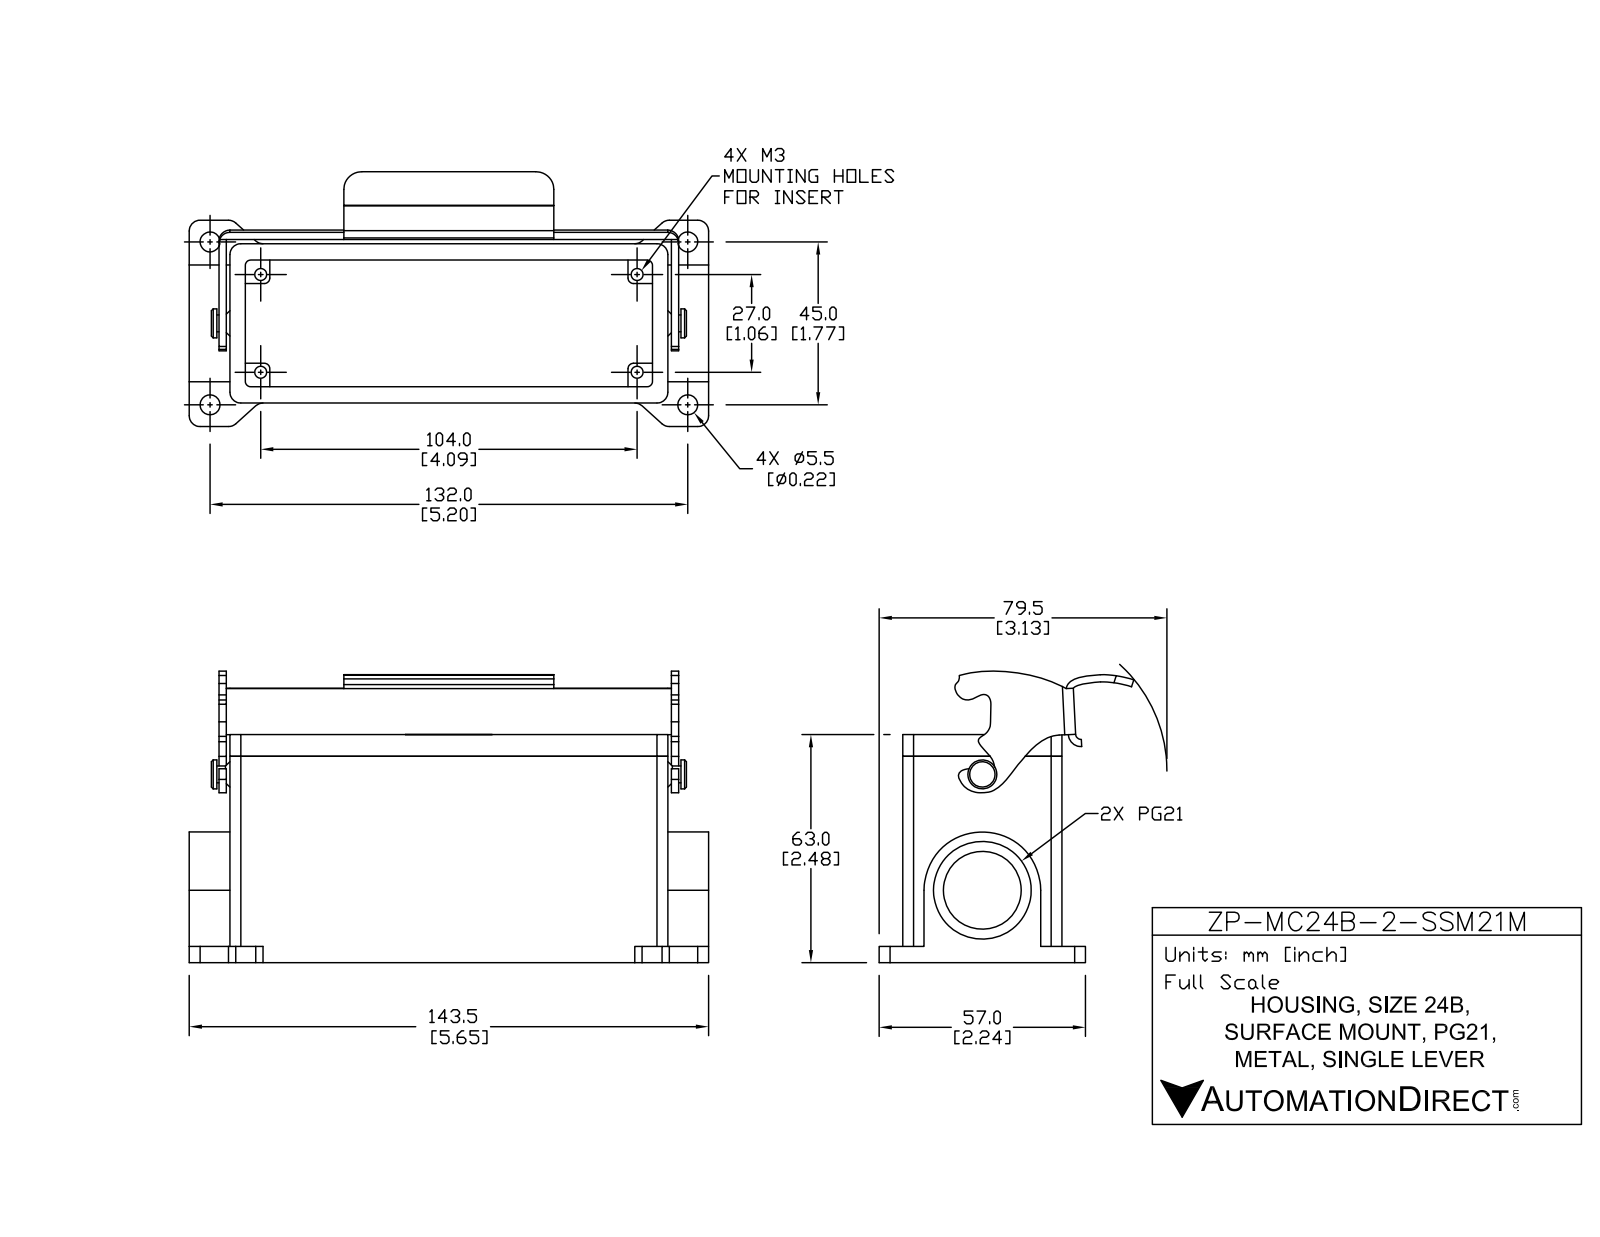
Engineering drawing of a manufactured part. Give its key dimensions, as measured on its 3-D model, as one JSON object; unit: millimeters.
{"part_name": "ZP-MC24B-2-SSM21M", "step_written_by": "SolidWorks 2011 (AUTOMOTIVE_DESIGN)", "units": "millimeters", "bodies": {"solids": 3, "faces": 205, "planar": 91, "cylindrical": 110, "other": 4}, "overall_size": [143.5, 77.44, 76.31], "volume_mm3": 116779, "surface_area_mm2": 65721, "round_holes": [[3.3, 4], [5.5, 4], [21.5, 1], [27, 1]], "round_bosses_or_shafts": [[8, 1], [4.67, 1]], "partial_cylinders_radius": [[3, 17], [0.5, 13], [1.5, 8], [2, 3], [4, 3], [1, 2], [10, 2], [0.92, 1]], "face_to_face_distances": [4.5, 39.5, 44, 35, 2, 57, 1.15, 55, 4.25, 116.75], "hole_center_spacings": [16.64, 38.63, 118.34, 123.37, 27, 45, 104, 107.45]}
